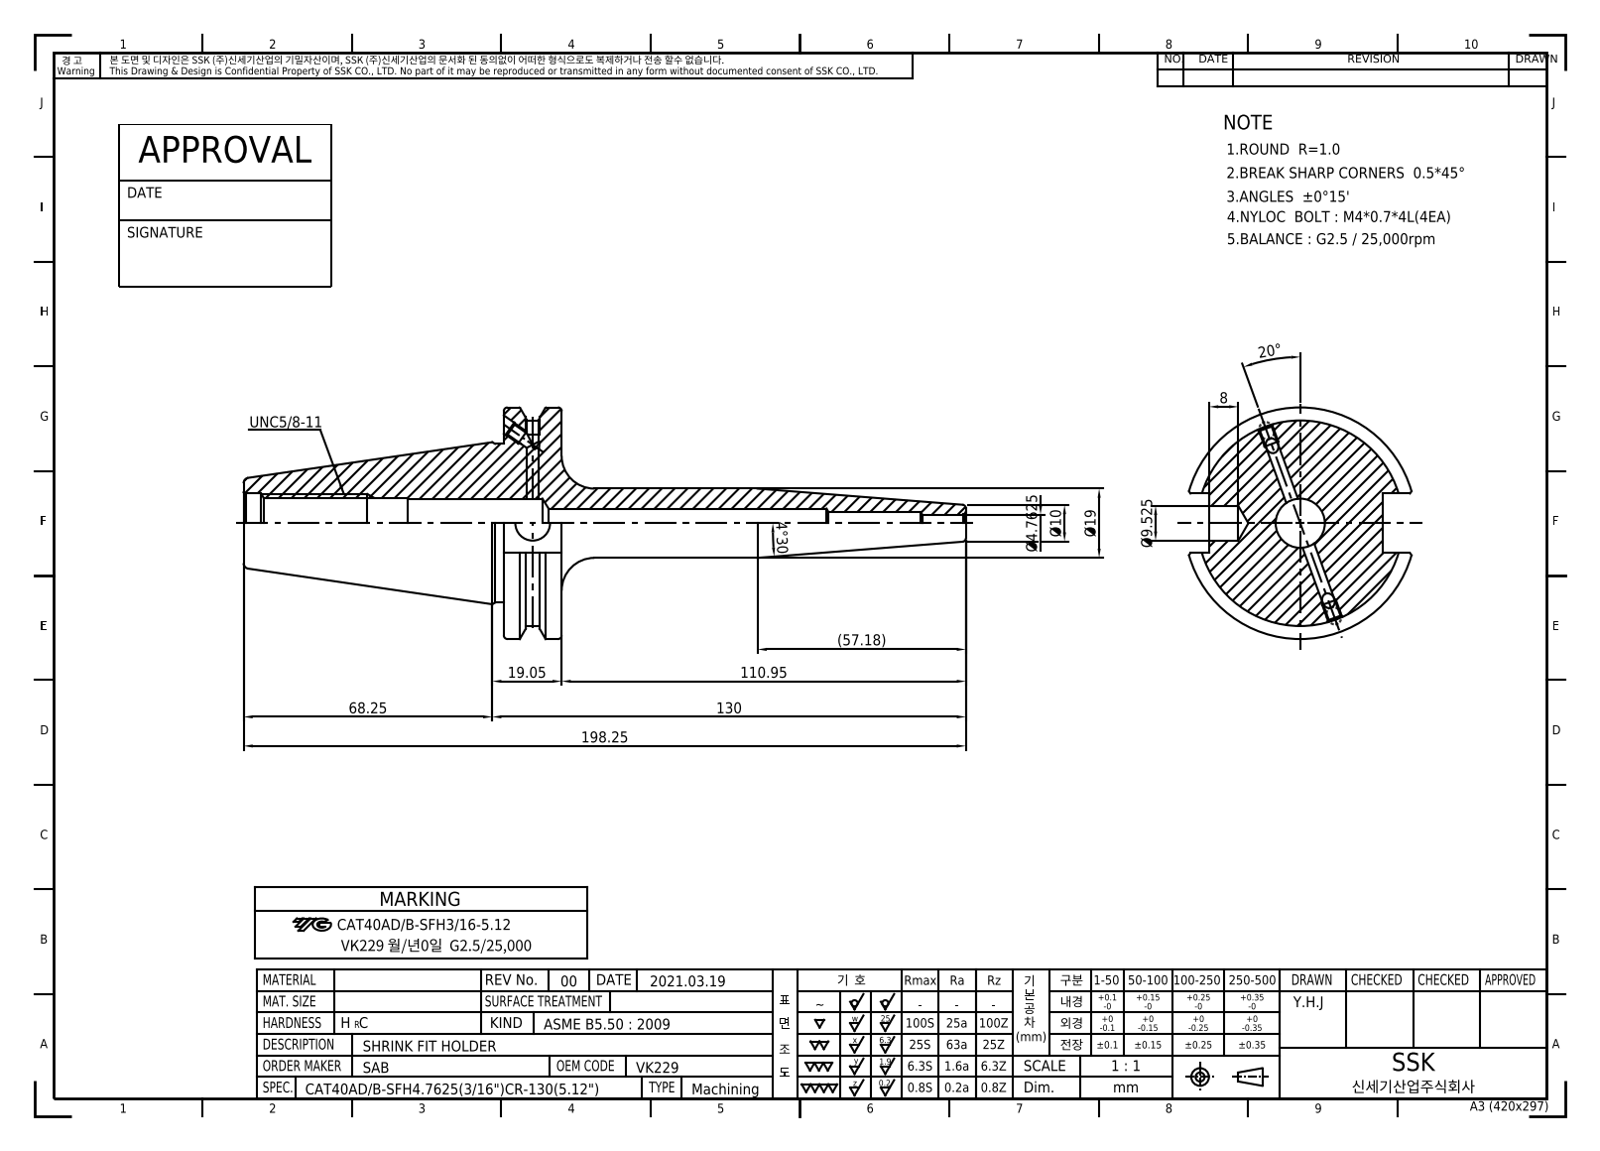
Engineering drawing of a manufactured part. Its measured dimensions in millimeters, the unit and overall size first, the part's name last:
Units: millimetres
Overall size (bounding box): 198.25 × 63.5 × 61.09
Round holes (diameter × count): ⌀3.24 ×4, ⌀4 ×2, ⌀4.2 ×2, ⌀4.76 ×1, ⌀6 ×1, ⌀8 ×1, ⌀9.53 ×1, ⌀13 ×1, ⌀13.39 ×1, ⌀16.3 ×1
Round bosses / shafts (diameter × count): ⌀63.5 ×1, ⌀43.6 ×1, ⌀19 ×1
Partial cylindrical surfaces — rounded edges, fillets, slot ends (radius × count): R28.15 ×1
Main face-to-face distances: 15.88, 47.6, 16.38, 71.42, 87.3, 77.47, 6.05, 9.83, 81.3, 9.88
Volume: 122 789 mm³ · Surface area: 28 658 mm²
Bodies: 1 solid, 87 faces (35 planar, 29 cylindrical, 23 other)
Part name (STEP PRODUCT): LO-CAT40ADB-SFH4.7625-130
STEP written by: Autodesk Inventor 2022 (AUTOMOTIVE_DESIGN)
